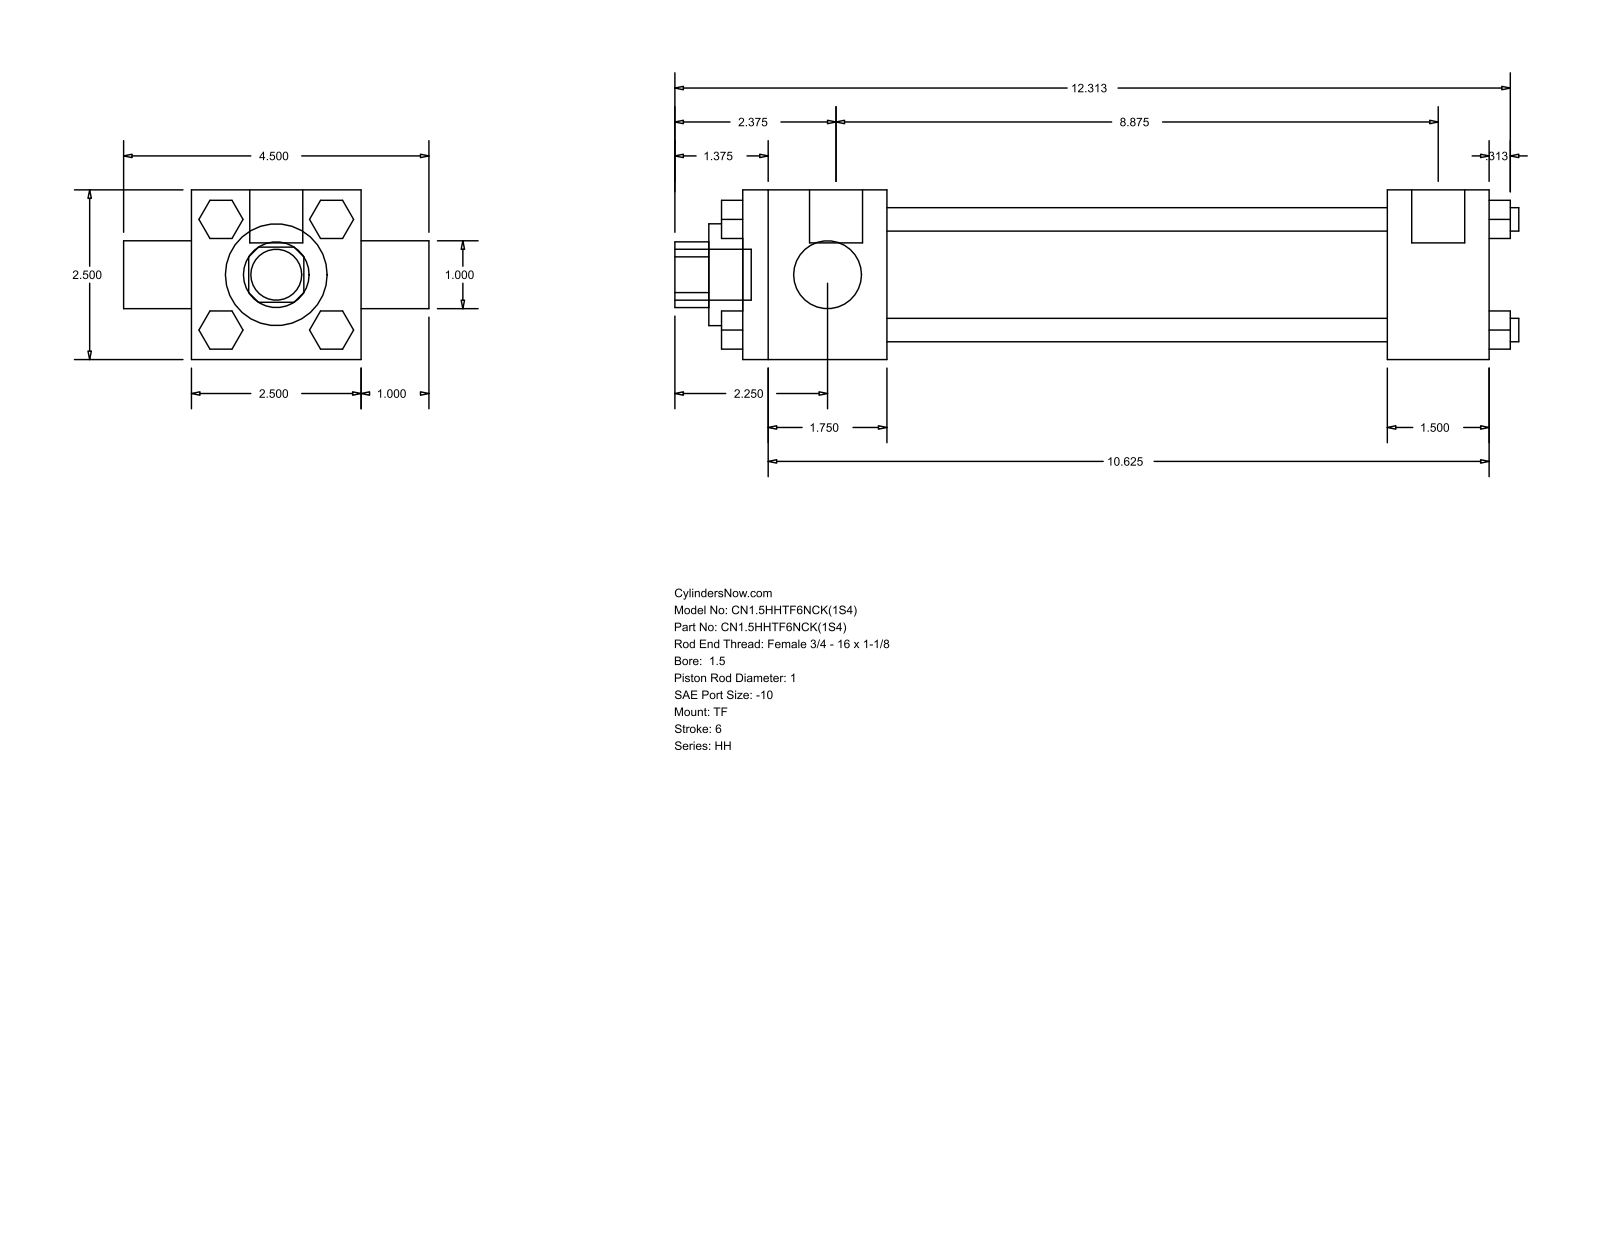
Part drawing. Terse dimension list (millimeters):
name: HH_TF__0150_1
written by: GSSL Pune (CONFIG_CONTROL_DESIGN)
unit: mm
bodies: 0 solids, 120 faces (92 planar, 28 cylindrical, 0 other)
size: 315.91 × 114.3 × 63.5
holes: 2× ⌀25.4, 1× ⌀38.1, 1× ⌀44.45
bosses: 4× ⌀8.76, 3× ⌀5.56, 2× ⌀19.84, 1× ⌀19.05
rounds: 1× R12.29
face distances: 63.5, 225.42, 187.32, 38.1, 53.98, 241.3, 279.4, 287.34, 25.4, 20.7
